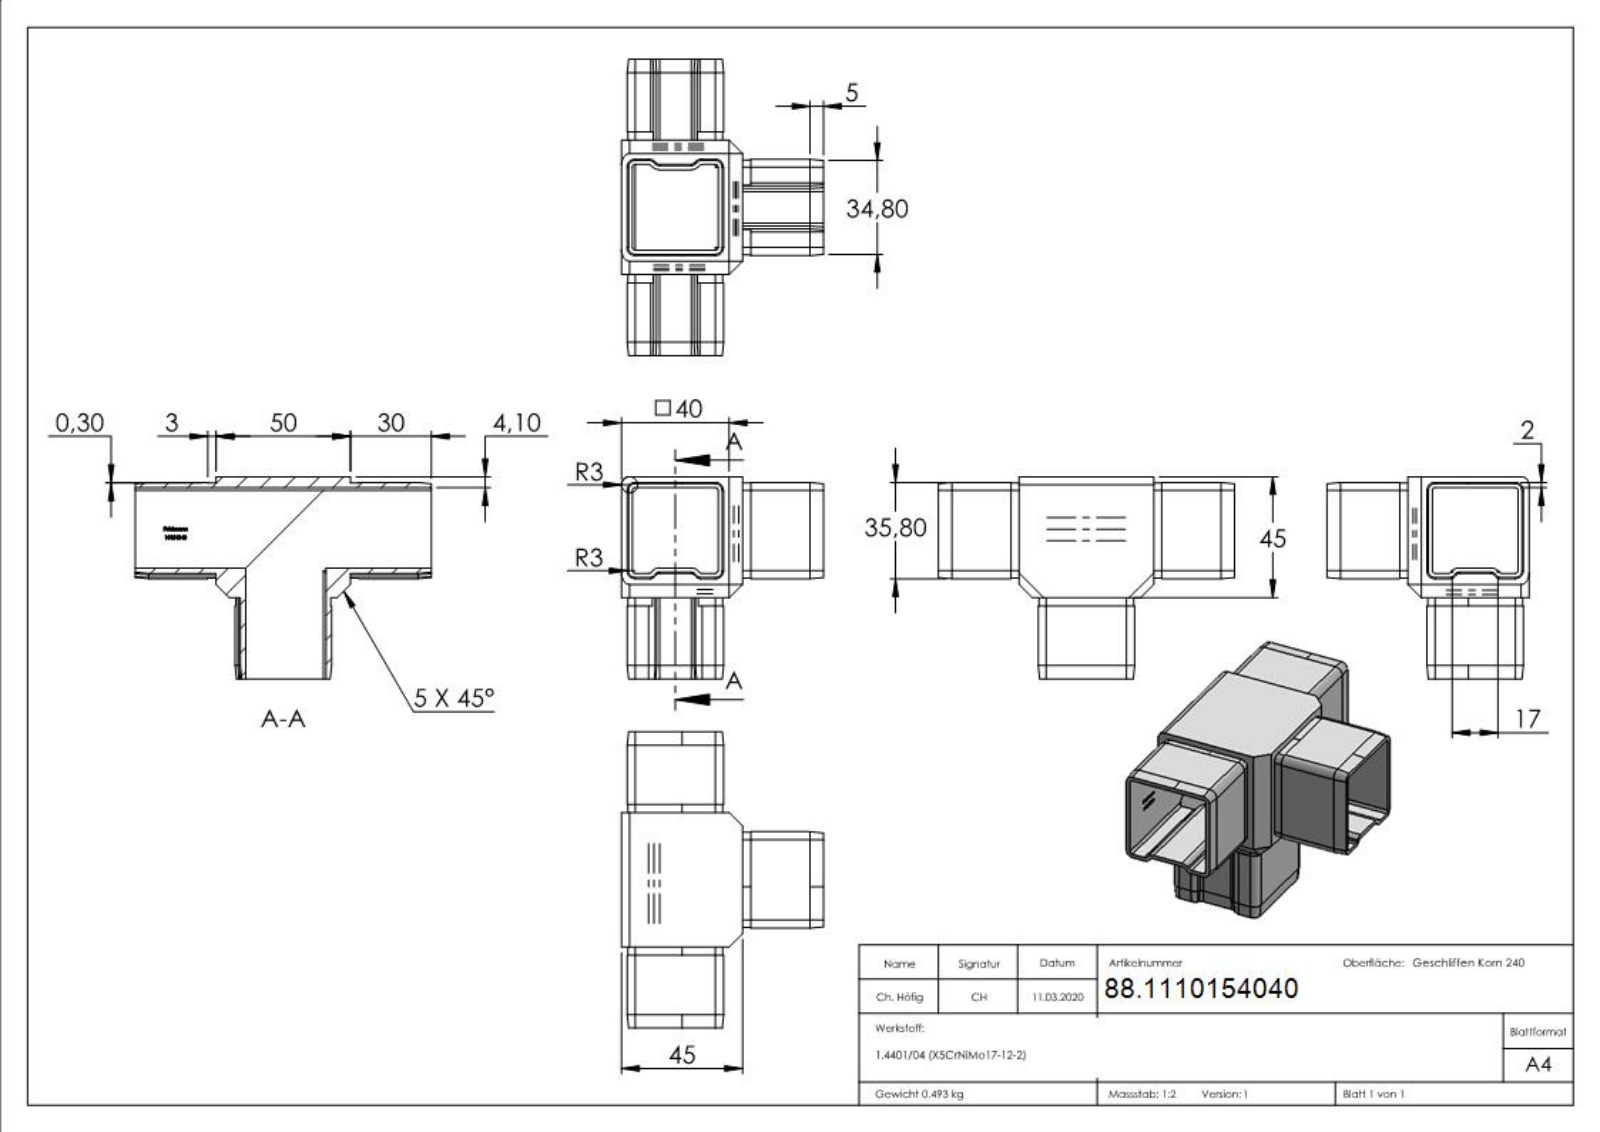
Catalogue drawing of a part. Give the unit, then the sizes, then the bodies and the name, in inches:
Units: inches
Overall size (bounding box): 4.331 × 2.953 × 2.953
Partial cylindrical surfaces — rounded edges, fillets, slot ends (radius × count): R0.059 ×16, R0.118 ×15, R0.039 ×12, R0.106 ×12, R0.138 ×8
Main face-to-face distances: 0.079, 1.252, 1.331, 0.161, 1.413, 0.083, 1.409, 1.492, 1.173, 1.689
Volume: 3.758 in³ · Surface area: 72.81 in²
Bodies: 1 solid, 497 faces (300 planar, 82 cylindrical, 115 other)
Part name (STEP PRODUCT): 10154040
STEP written by: SolidWorks 2015 (CONFIG_CONTROL_DESIGN)
